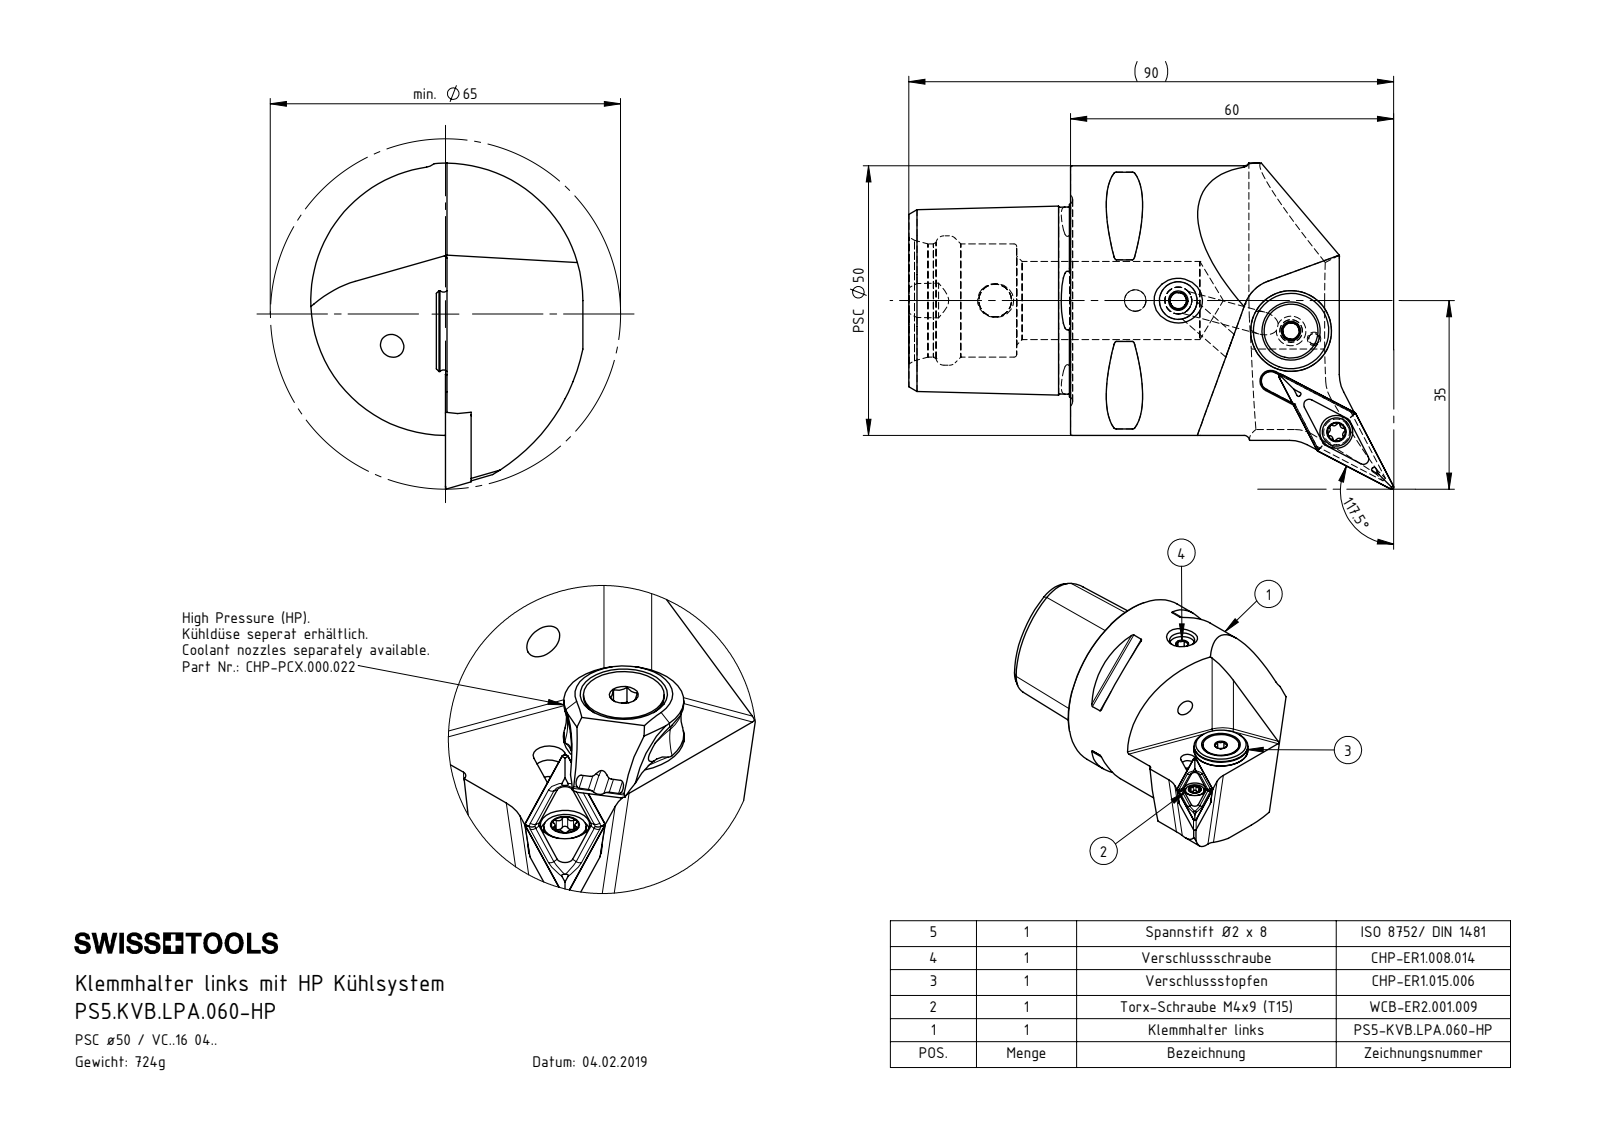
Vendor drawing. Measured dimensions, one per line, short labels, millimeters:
name: DIN 3771 - 13x1; ISO 8752 2x8; PS5.KVB.LPA.060-HP; DIN 7991 - M5x15 (+6 more)
written by: SolidWorks 2017 (AUTOMOTIVE_DESIGN)
unit: mm
bodies: 8 solids, 279 faces (94 planar, 63 cylindrical, 122 other)
size: 90 × 60.5 × 50.5
volume: 91 716 mm³; area: 21 647 mm²
holes: 3× ⌀4.2, 2× ⌀6.1, 1× ⌀1.2, 1× ⌀2, 1× ⌀2.5, 1× ⌀3, 1× ⌀3.3, 1× ⌀4, 1× ⌀4.4, 1× ⌀5, 1× ⌀5.2, 1× ⌀7
bosses: 1× ⌀50, 1× ⌀15, 1× ⌀13.4, 1× ⌀10, 1× ⌀8, 1× ⌀5.5, 1× ⌀5.25, 1× ⌀5
rounds: 10× R0.5, 6× R0.34, 6× R0.59, 3× R7, 1× R1.75, 1× R4, 1× R25.5, 1× R35
face distances: 30, 4.5, 4.46, 19.18, 44.4, 20.7, 20.74, 25.2, 10, 20
hole spacings: 4.49, 8, 17.72, 17.77, 20.49, 20.54, 21.69, 26
